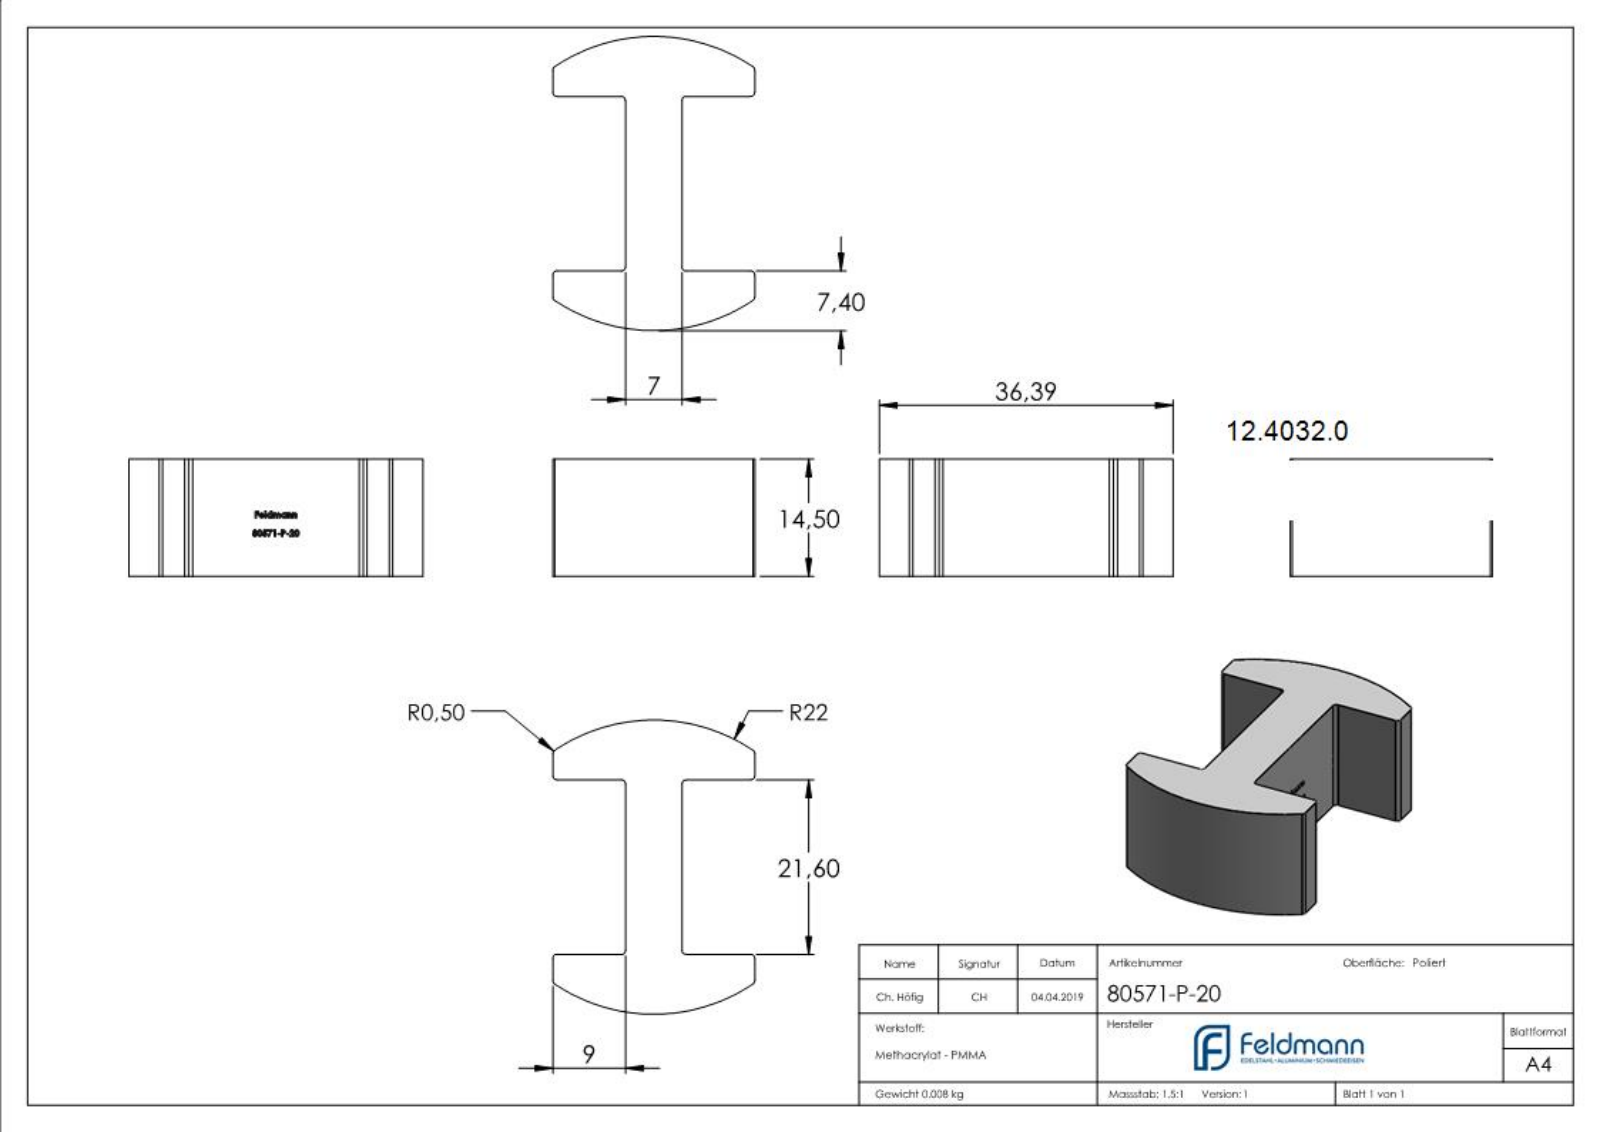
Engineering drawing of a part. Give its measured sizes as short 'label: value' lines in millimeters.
name: 80571-P-20
written by: SolidWorks 2015 (CONFIG_CONTROL_DESIGN)
unit: mm
bodies: 1 solid, 251 faces (135 planar, 15 cylindrical, 101 other)
size: 36.39 × 25 × 14.5
volume: 6 648 mm³; area: 3 018 mm²
rounds: 12× R0.5, 2× R22
face distances: 14.5, 7, 21.6, 9, 16, 25, 15.9, 6.9, 9.1, 7.25
